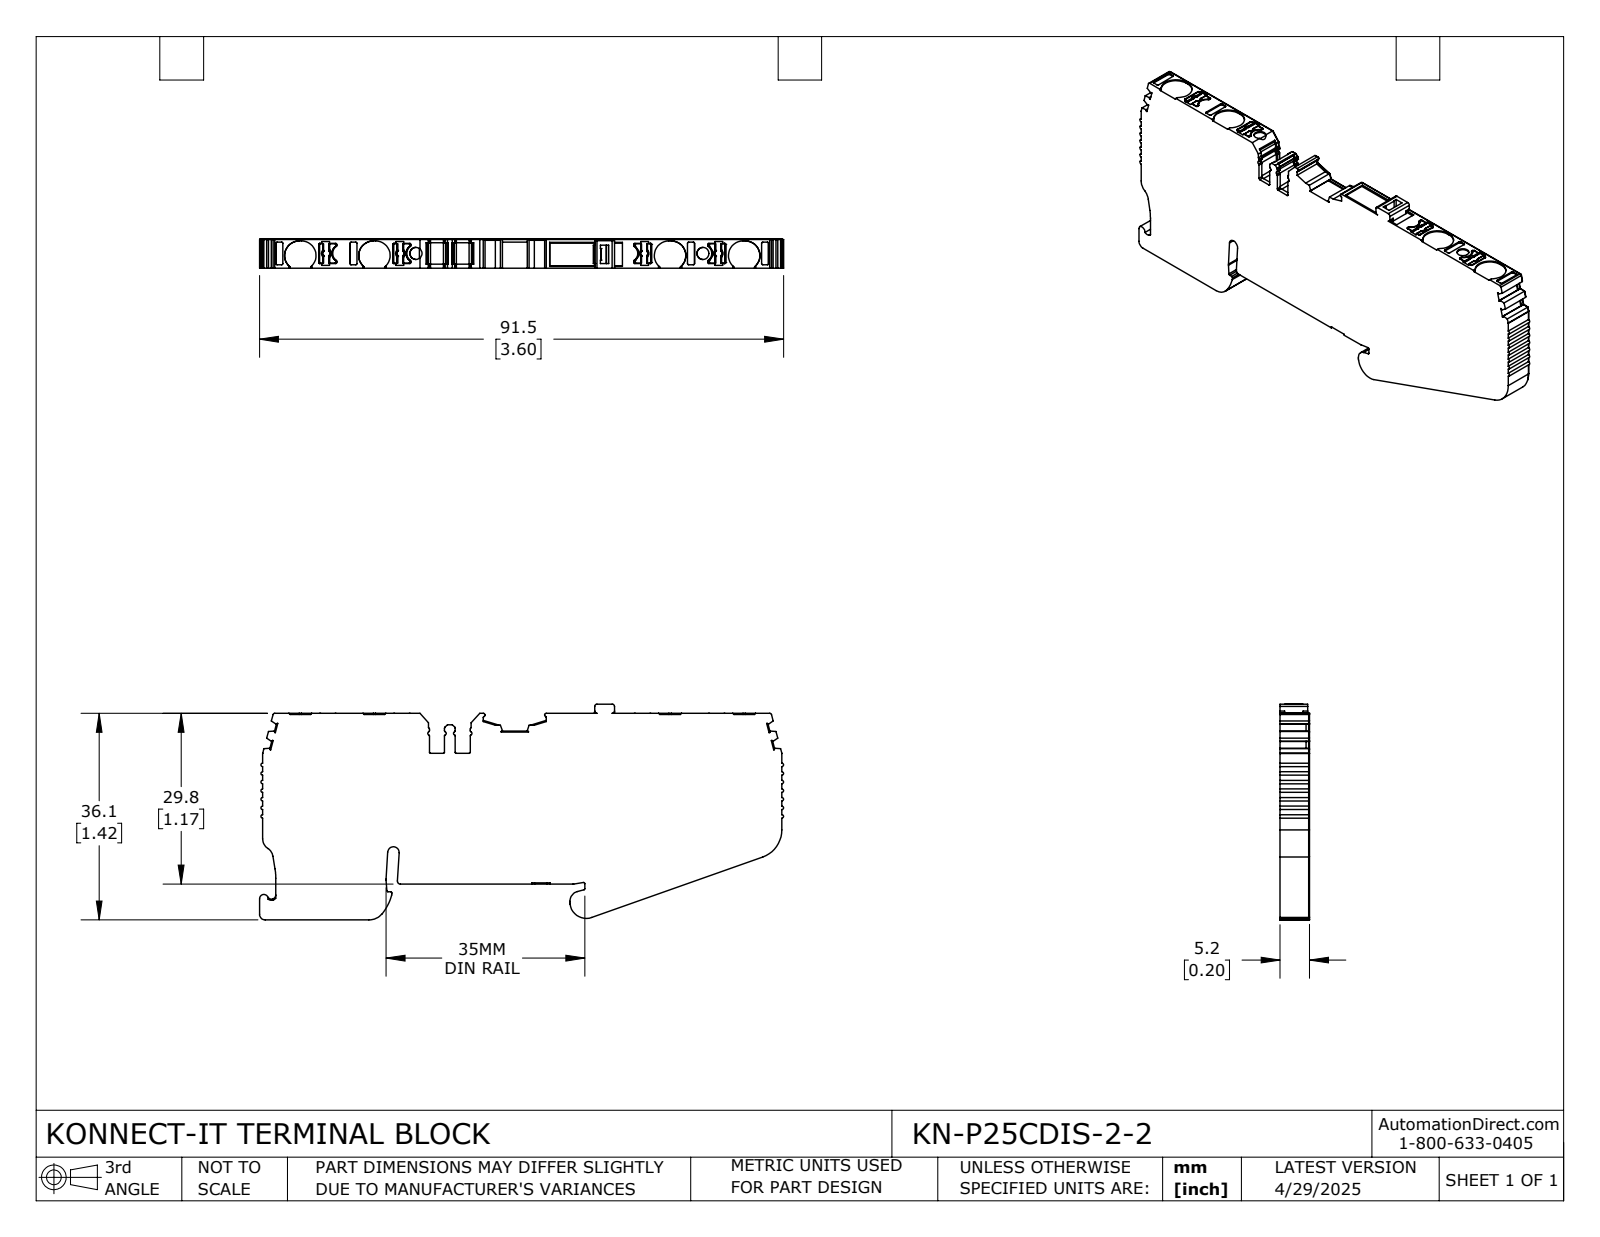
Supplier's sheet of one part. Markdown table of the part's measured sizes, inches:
| quantity | value |
| --- | --- |
| part name | KN-P25CDIS-2-2 |
| STEP written by | SolidWorks 2024 (CONFIG_CONTROL_DESIGN) |
| units | inches |
| bodies | 1 solid, 774 faces (405 planar, 298 cylindrical, 71 other) |
| overall size | 3.602 × 1.483 × 0.203 |
| volume | 0.856 in³ |
| surface area | 11.15 in² |
| round holes (diameter × count) | 0.083 × 2 |
| partial cylindrical surfaces (radius × count) | 0.008 × 78, 0.012 × 39, 0.004 × 21, 0.02 × 18, 0.006 × 16, 0.016 × 13, 0.1 × 8, 0.039 × 4 |
| main face-to-face distances | 0.203, 1.166, 1.174, 0.246, 1.412, 1.42, 3.569, 0.197, 0.177, 0.047 |
| hole center spacings | 1.973 |
